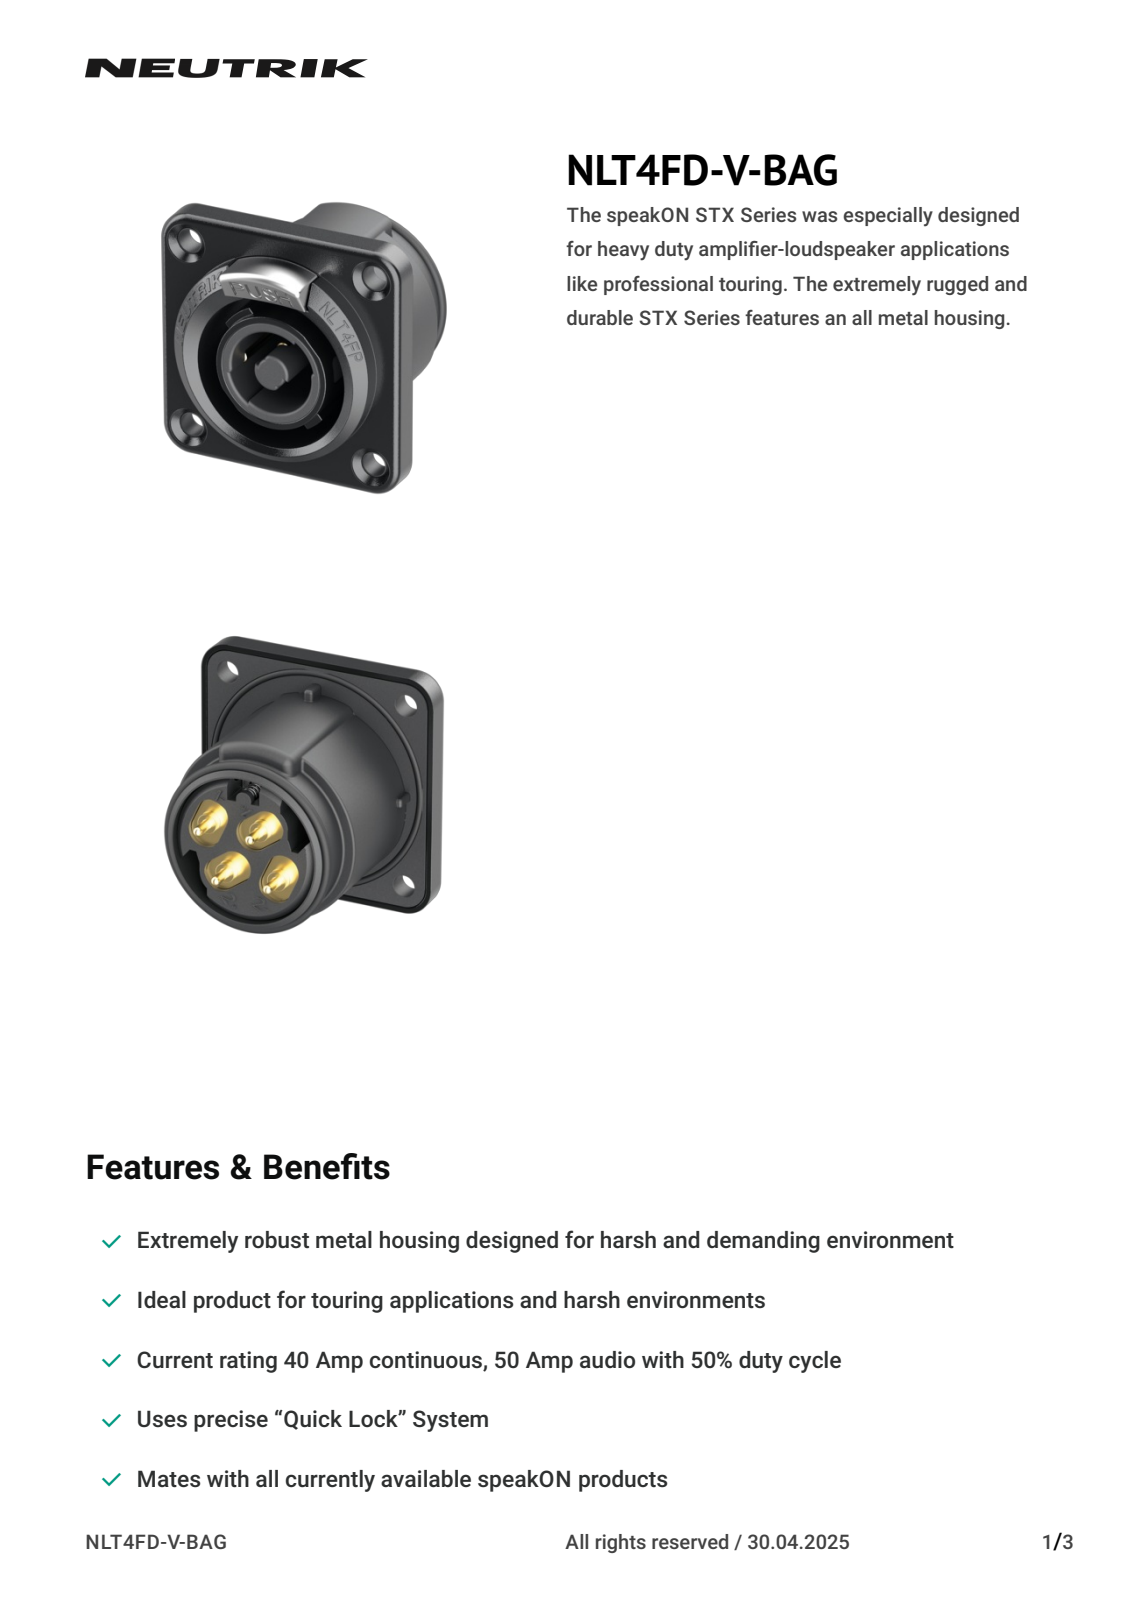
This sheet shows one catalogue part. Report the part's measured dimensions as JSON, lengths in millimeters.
{"part_name": "30011067", "step_written_by": "CREO PARAMETRIC BY PTC INC, 2023424 (CONFIG_CONTROL_DESIGN)", "units": "millimeters", "bodies": {"solids": 2, "faces": 783, "planar": 368, "cylindrical": 177, "other": 238}, "overall_size": [39.7, 38, 38], "volume_mm3": 17724, "surface_area_mm2": 10786, "round_holes": [[3.5, 4], [4, 4], [6, 4], [12.5, 1]], "round_bosses_or_shafts": [[3.9, 4], [3, 4], [1.45, 4], [25.6, 1], [25, 1], [24, 1], [5.5, 1]], "partial_cylinders_radius": [[0.2, 32], [0.5, 26], [1, 8], [1.5, 4], [0.8, 2], [0.9, 2], [1.2, 2], [3.48, 2]], "face_to_face_distances": [4.5, 23.6, 28.1, 10.6, 13, 17.5, 2.5, 20, 30.6, 7], "hole_center_spacings": [29.2, 19.45, 21.92, 41.3]}
